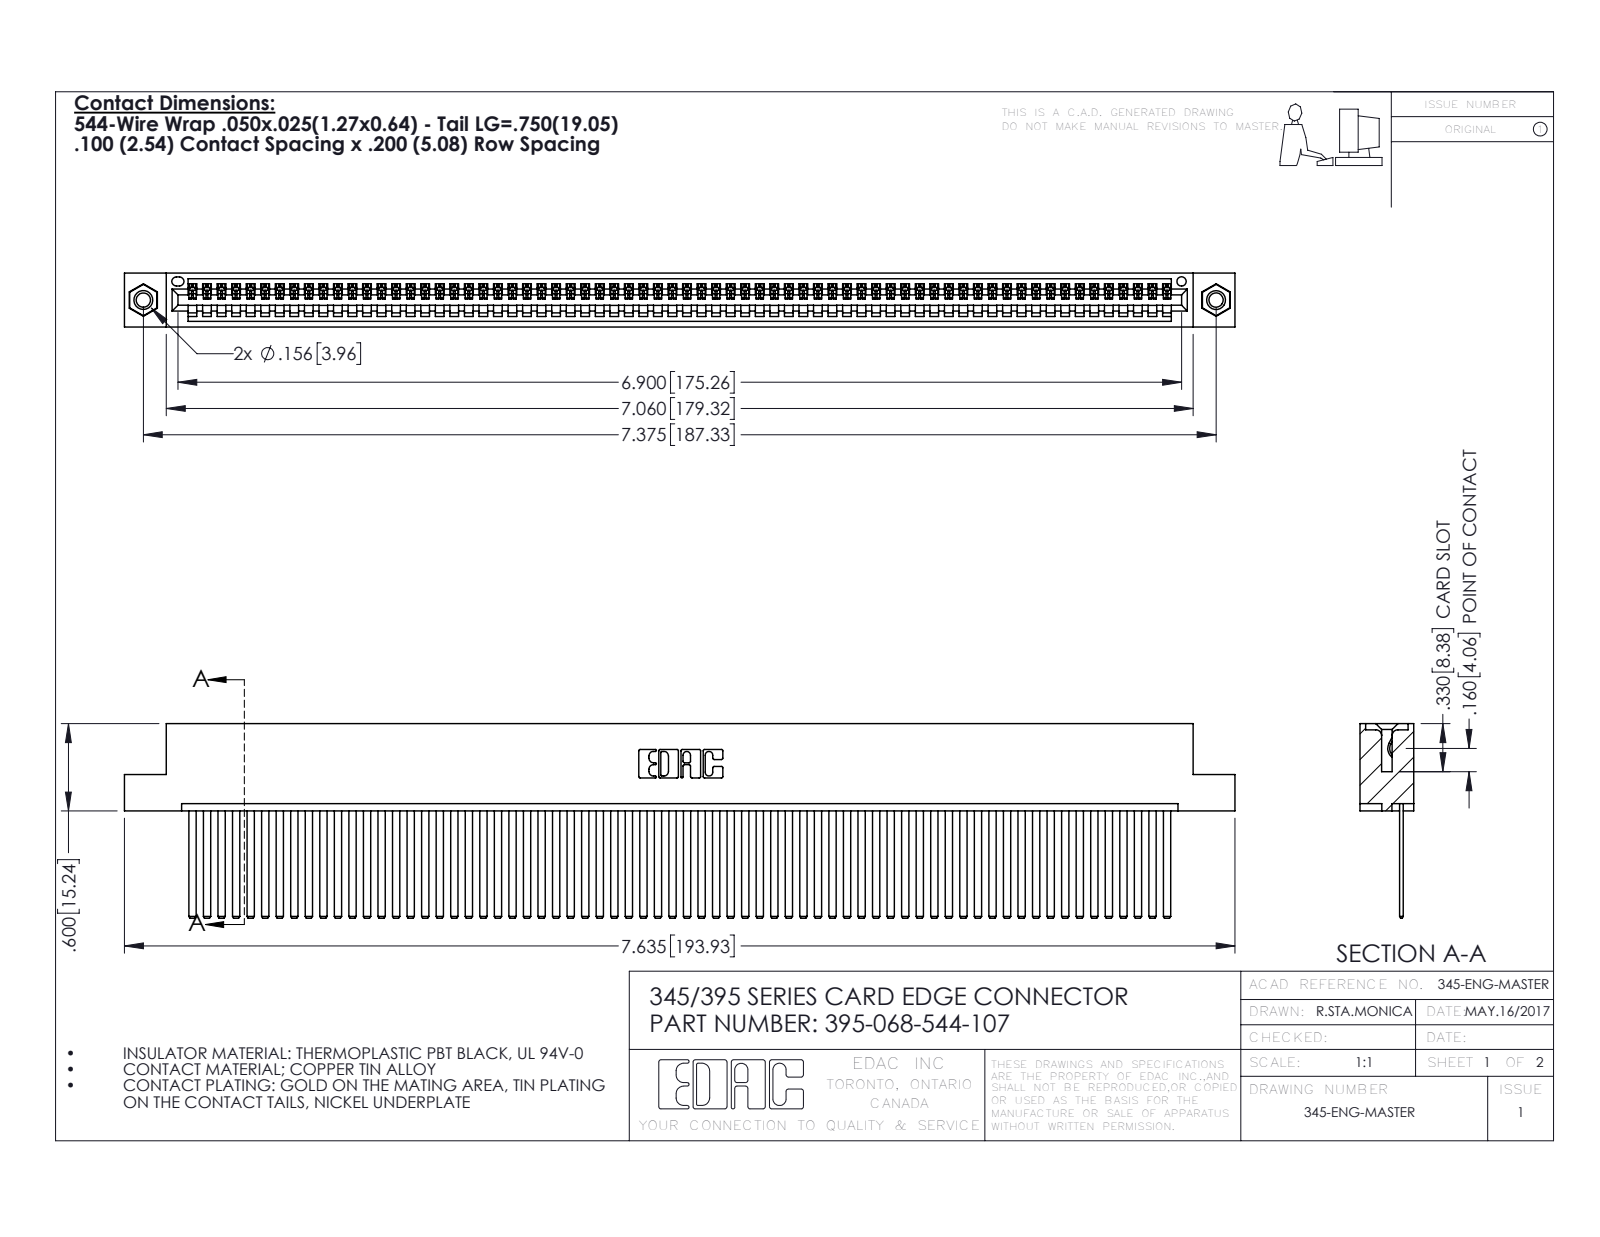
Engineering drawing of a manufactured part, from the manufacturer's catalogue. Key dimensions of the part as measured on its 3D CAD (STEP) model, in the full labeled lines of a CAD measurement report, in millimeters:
Part name (STEP PRODUCT): 345-250-001_345-250-005-103; 345-292-001_345-293-144; 345 Part_Flush Mounting Lugs - 0.156 Dia-TI; 395-068-544-107
STEP written by: SolidWorks 2016 (CONFIG_CONTROL_DESIGN)
Units: millimetres
Bodies: 71 solids, 3722 faces (2560 planar, 1146 cylindrical, 16 other)
Overall size (bounding box): 193.9 × 34 × 9.4
Volume: 19 400 mm³ · Surface area: 28 540 mm²
Round holes (diameter × count): ⌀2.5 ×2, ⌀3.2 ×2, ⌀4 ×2, ⌀1.6 ×1
Round bosses / shafts (diameter × count): ⌀3.9 ×2
Partial cylindrical surfaces — rounded edges, fillets, slot ends (radius × count): R0.2 ×136, R0.3 ×22, R0.2 ×6, R0.8 ×6, R0.7 ×3, R0.8 ×2, R1 ×2, R0.4 ×1
Main face-to-face distances: 1.8, 7.6, 0.6, 2.5, 6.9, 9.4, 5.1, 5.7, 3.8, 1.8
Hole centre spacings: 6.9, 181.3, 187.3
